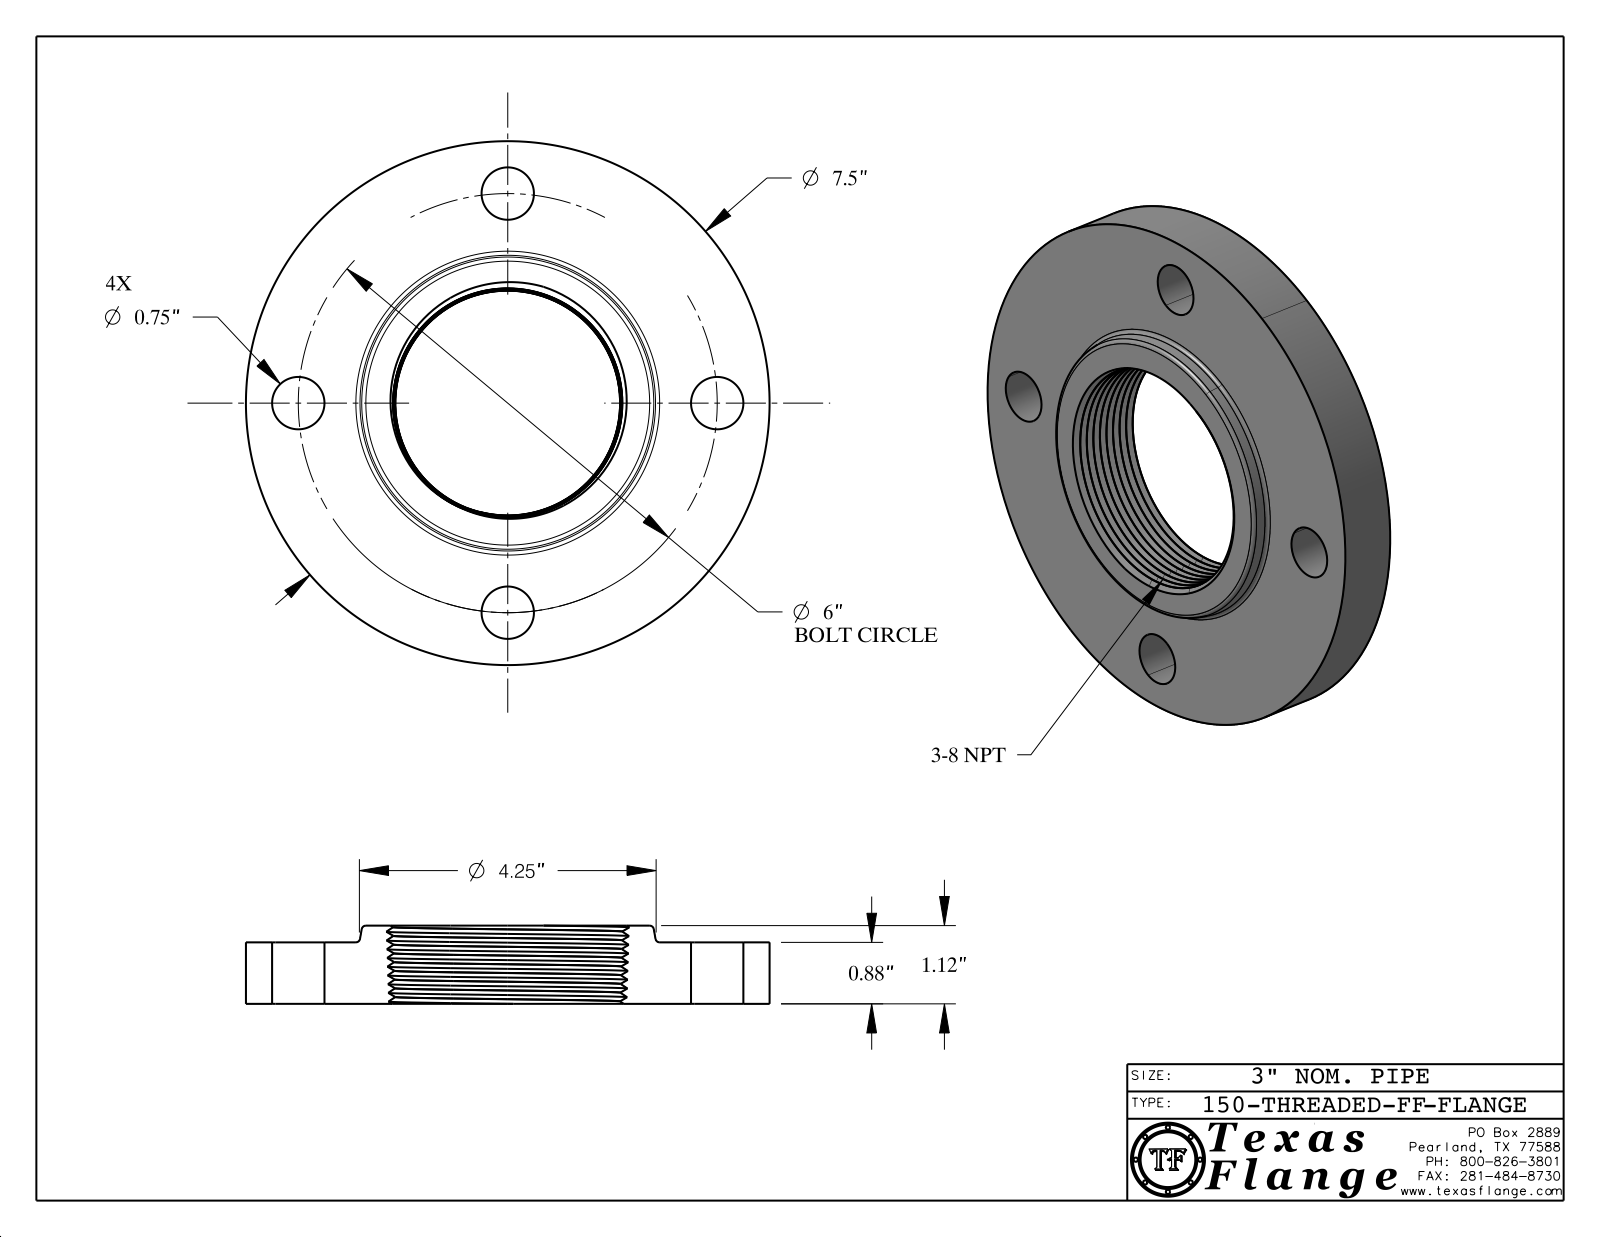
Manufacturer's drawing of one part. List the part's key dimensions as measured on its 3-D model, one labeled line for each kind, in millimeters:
Part name (STEP PRODUCT): 150-THREADED-FF
STEP written by: CATIA V5 STEP AP214 (AUTOMOTIVE_DESIGN)
Units: millimetres
Bodies: 1 solid, 501 faces (368 planar, 30 cylindrical, 103 other)
Overall size (bounding box): 190.5 × 190.5 × 28.4
Volume: 504 600 mm³ · Surface area: 77 810 mm²
Round holes (diameter × count): ⌀19.1 ×4, ⌀12.6 ×1
Round bosses / shafts (diameter × count): ⌀0.8 ×8, ⌀190.5 ×1, ⌀9.9 ×1
Main face-to-face distances: 22.4, 28.4, 6.1, 22, 0.4, 6.5, 3.8, 3.7, 0.7, 3.1
Hole centre spacings: 107.8, 58.3, 140.8, 152.4
